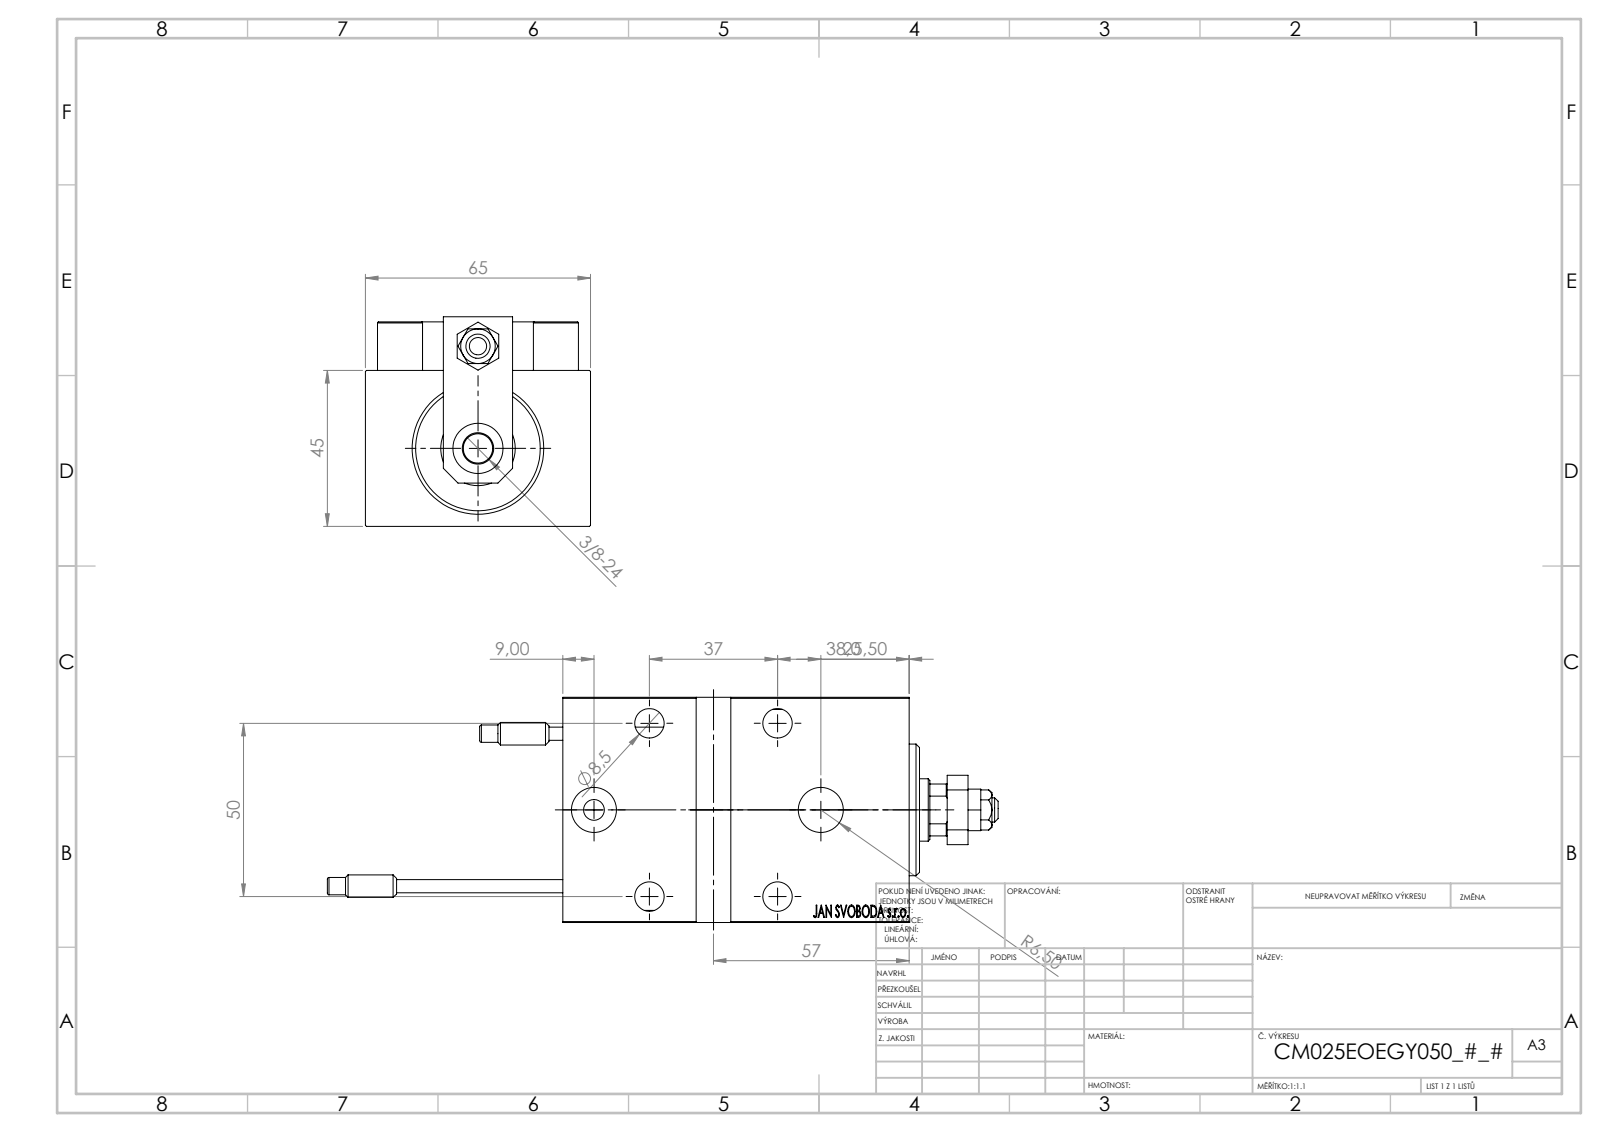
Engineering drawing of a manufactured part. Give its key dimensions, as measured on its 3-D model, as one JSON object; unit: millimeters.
{"part_name": "SWITCH X; TYC_L79; ALLEN BOLT D5; SWITCH_X_FRONT_BACK (+7 more)", "step_written_by": "SolidWorks 2019 (CONFIG_CONTROL_DESIGN)", "units": "millimeters", "bodies": {"solids": 24, "faces": 1308, "planar": 571, "cylindrical": 184, "other": 553}, "overall_size": [193.7, 65, 60.5], "volume_mm3": 318842, "surface_area_mm2": 78410, "round_holes": [[8, 5], [8.5, 5], [3.2, 4], [4, 4], [13.5, 4], [5, 2], [13, 2], [7, 1], [14.5, 1], [18, 1], [21.5, 1], [25, 1]], "round_bosses_or_shafts": [[5, 4], [6.5, 2], [3.8, 2], [38, 1], [27, 1], [13, 1], [11, 1], [6, 1]], "partial_cylinders_radius": [[0.3, 30], [3, 2], [8.5, 1]], "face_to_face_distances": [45, 65, 14, 59, 6, 100, 13, 111, 10, 5], "hole_center_spacings": [40.31, 10.77, 11.37, 20, 21.03, 25, 27.95, 29.59]}
